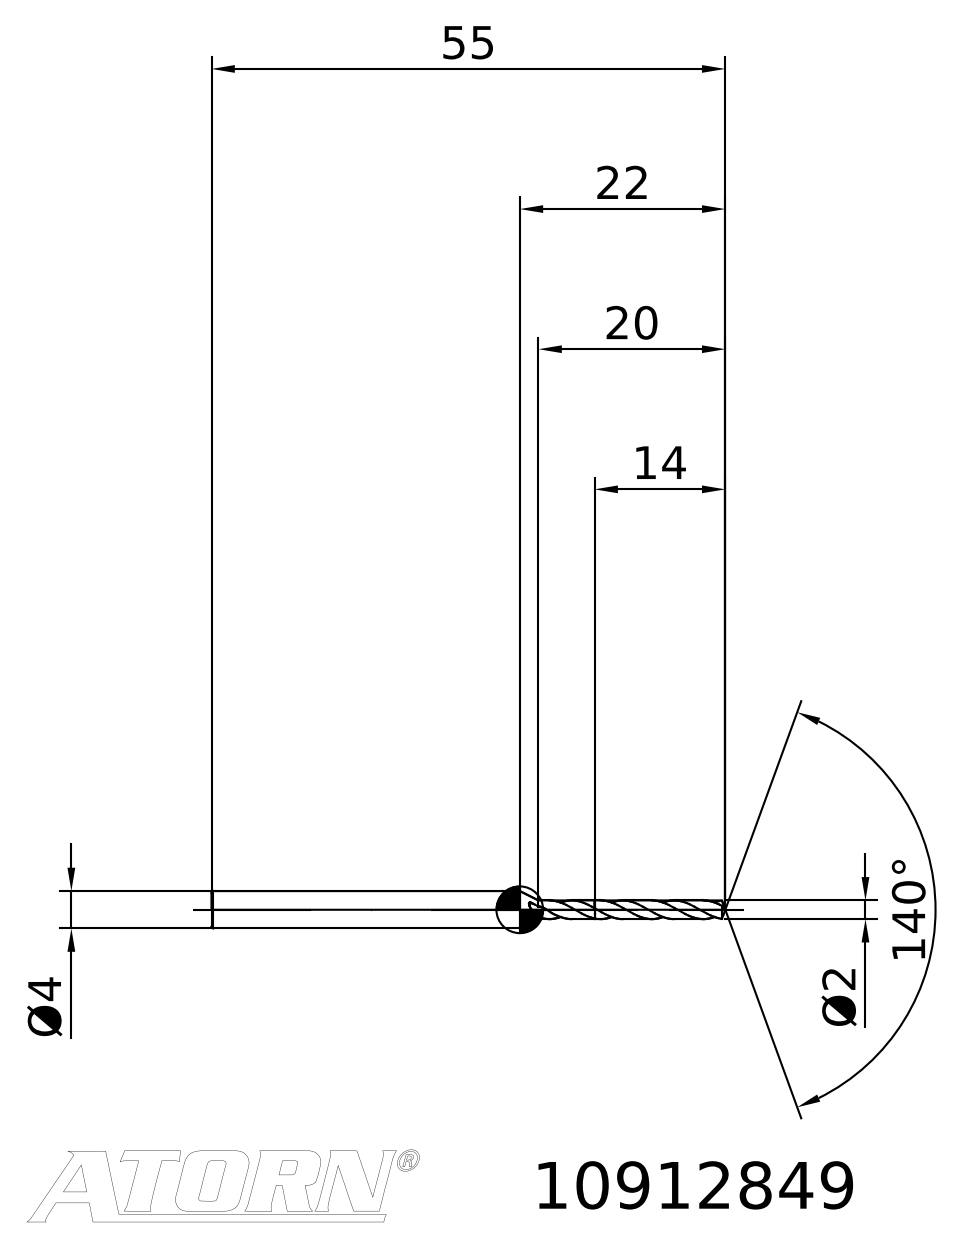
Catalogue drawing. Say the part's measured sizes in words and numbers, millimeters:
Its 3-D file was written by "TDM (AUTOMOTIVE_DESIGN)". It is 2 solids with 30 faces: 3 planar, 0 cylindrical and 27 other. Overall it measures 55 by 6.85 by 4 millimeters. Its volume is 470 cubic millimeters and its surface area 589 square millimeters. The main face-to-face distances are 41.
